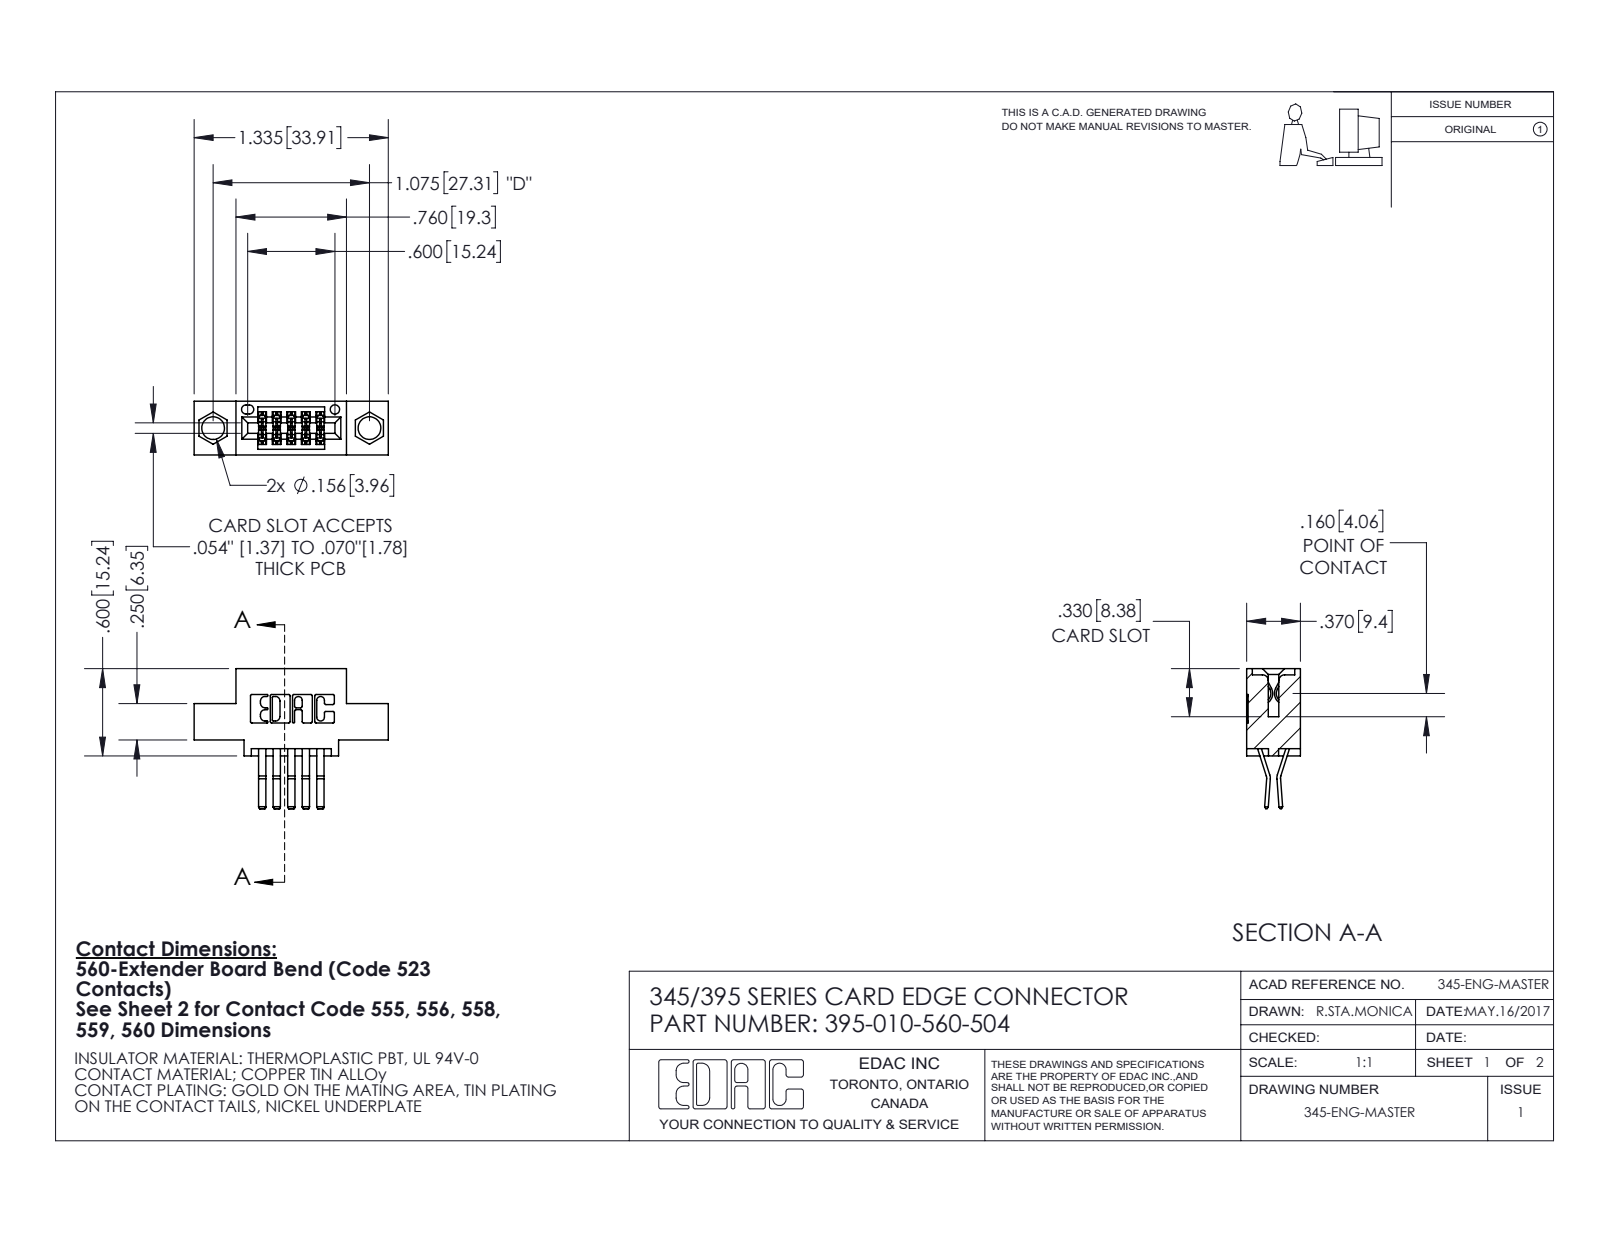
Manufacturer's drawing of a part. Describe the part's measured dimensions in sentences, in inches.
The part is named "345-292-001_560 Tail; 395-010-560-504; 345 Part_0.110 Offset - 0.156 Dia-TI". Its 3-D file was written by "SolidWorks 2020 (CONFIG_CONTROL_DESIGN)". It is 11 solids with 664 faces: 428 planar, 236 cylindrical and 0 other. Overall it measures 1.335 by 0.962 by 0.37 inches. Its volume is 0.173 cubic inches and its surface area 5.564 square inches. Round holes: 2 of diameter 0.156, 1 of diameter 0.064. Partial cylindrical surfaces (rounded edges, fillets, slot ends): 22 of radius 0.01, 15 of radius 0.006, 6 of radius 0.007, 6 of radius 0.031, 3 of radius 0.026, 2 of radius 0.01, 2 of radius 0.014, 2 of radius 0.019. The main face-to-face distances are 0.2, 0.37, 0.1, 0.025, 0.298, 0.072, 0.25, 0.098, 0.272, 0.15. The hole center spacings are 0.27, 0.847, 1.075.
